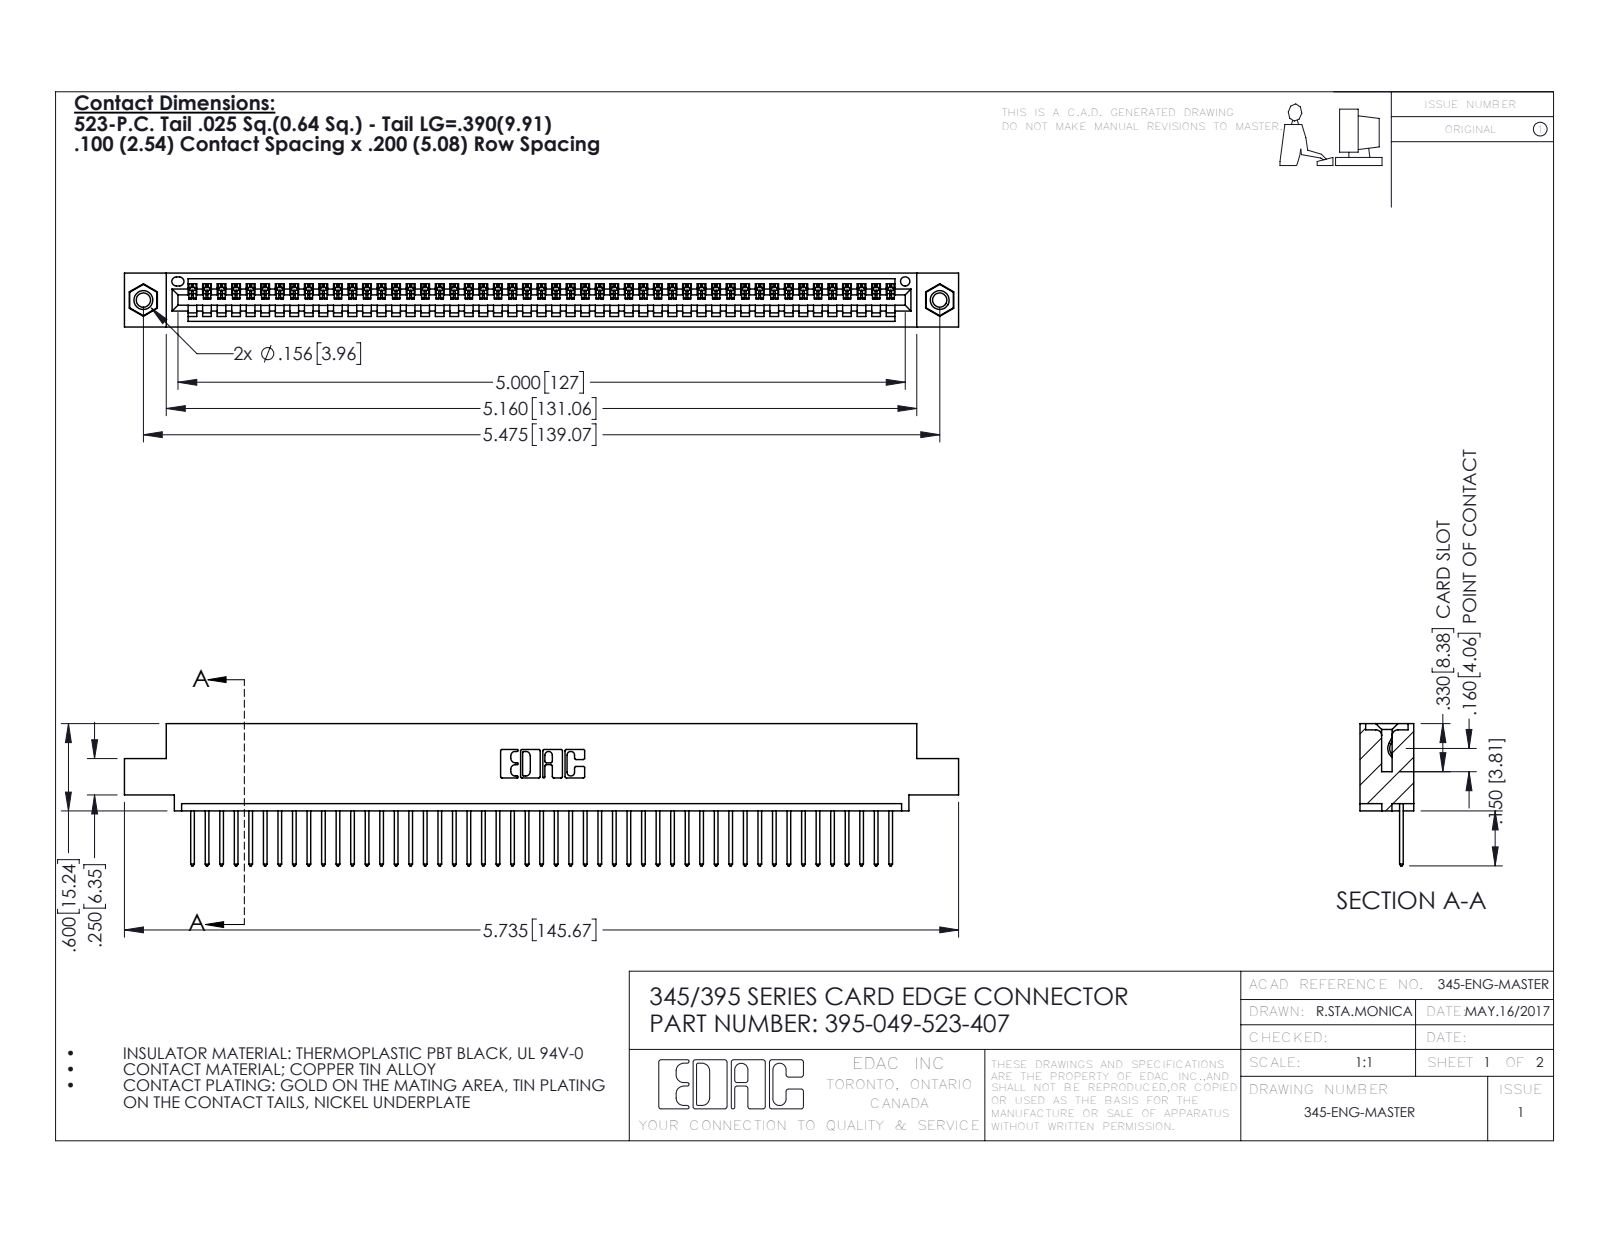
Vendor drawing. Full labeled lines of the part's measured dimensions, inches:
Part name (STEP PRODUCT): 345-250-001_345-250-005-103; 345-292-001_345-293-123; 345 Part_0.110 Offset - 0.156 Dia-TI; 395-049-523-407
STEP written by: SolidWorks 2016 (CONFIG_CONTROL_DESIGN)
Units: inches
Bodies: 52 solids, 3032 faces (2076 planar, 940 cylindrical, 16 other)
Overall size (bounding box): 5.735 × 0.977 × 0.37
Volume: 0.841 in³ · Surface area: 28.81 in²
Round holes (diameter × count): ⌀0.098 ×2, ⌀0.125 ×2, ⌀0.156 ×2, ⌀0.064 ×1
Round bosses / shafts (diameter × count): ⌀0.155 ×2
Partial cylindrical surfaces — rounded edges, fillets, slot ends (radius × count): R0.006 ×98, R0.01 ×98, R0.01 ×22, R0.007 ×6, R0.031 ×6, R0.026 ×3, R0.031 ×2, R0.04 ×2
Main face-to-face distances: 0.072, 0.298, 0.37, 0.2, 0.098, 0.272, 0.025, 0.225, 0.149, 0.072
Hole centre spacings: 0.27, 5.239, 5.475
